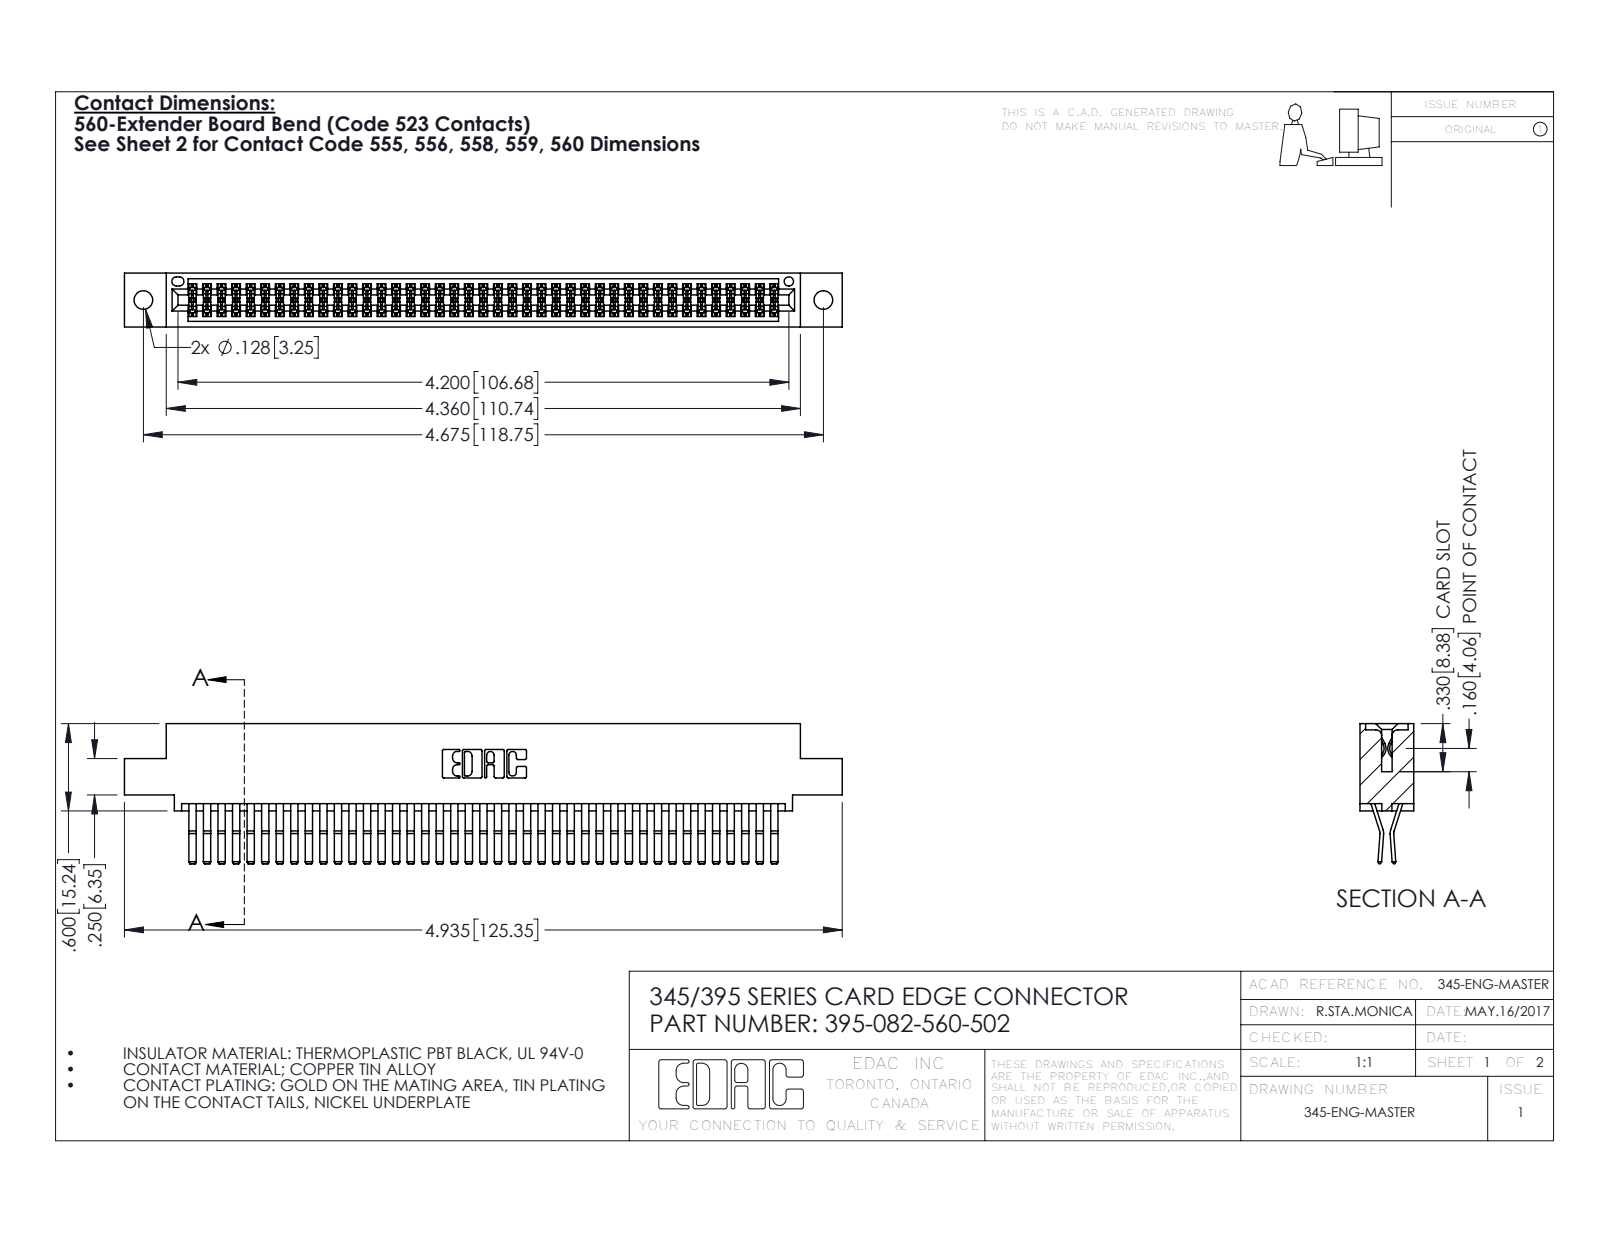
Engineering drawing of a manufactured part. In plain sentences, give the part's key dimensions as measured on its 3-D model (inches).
The part is named "395-082-560-502; 345-292-001_560 Tail; 345 Part_0.110 Offset - 0.128 Dia". Its 3-D file was written by "SolidWorks 2016 (CONFIG_CONTROL_DESIGN)". It is 83 solids with 4394 faces: 2790 planar, 1604 cylindrical and 0 other. Overall it measures 4.935 by 0.962 by 0.37 inches. Its volume is 0.769 cubic inches and its surface area 30.69 square inches. Round holes: 2 of diameter 0.128, 1 of diameter 0.064. Partial cylindrical surfaces (rounded edges, fillets, slot ends): 123 of radius 0.006, 22 of radius 0.01, 6 of radius 0.007, 6 of radius 0.031, 3 of radius 0.026, 2 of radius 0.01, 2 of radius 0.014, 2 of radius 0.019. The main face-to-face distances are 0.025, 0.298, 0.072, 0.37, 0.2, 0.098, 0.272, 0.225, 0.175, 0.149. The hole center spacings are 0.27, 4.439, 4.675.
